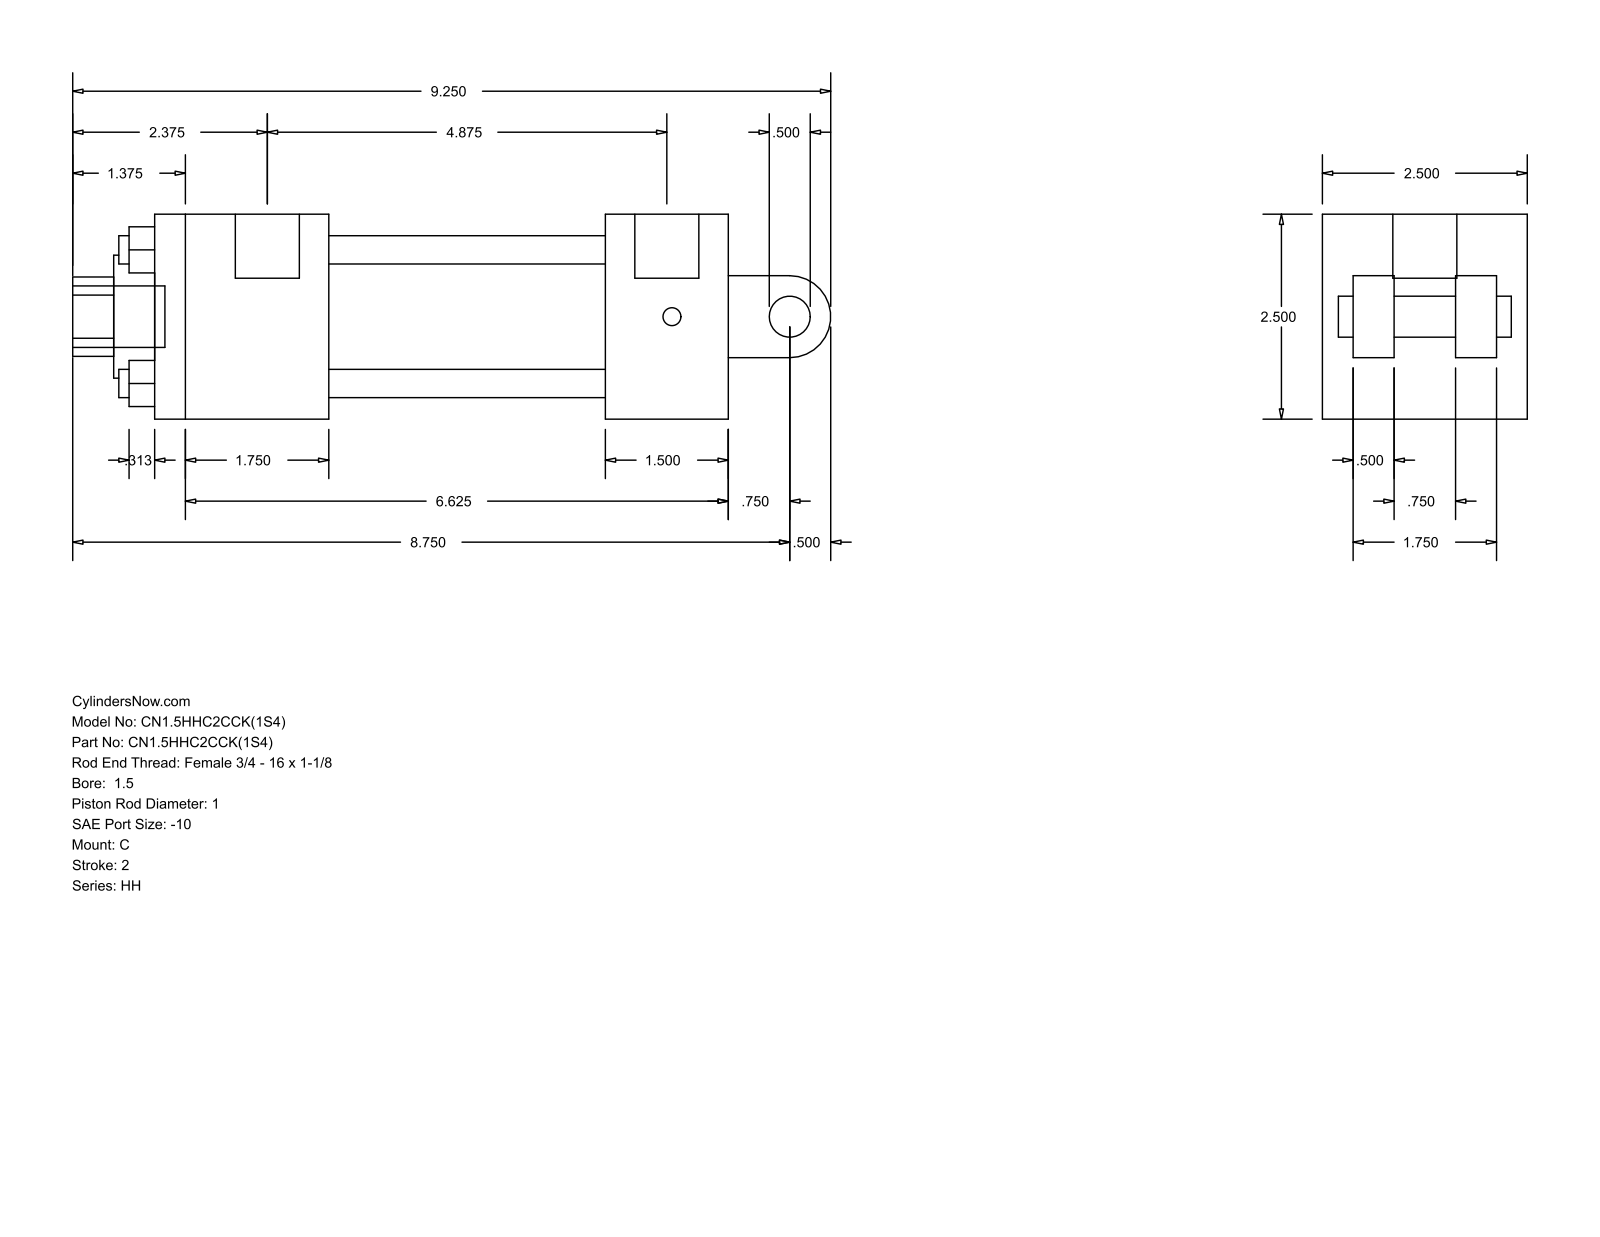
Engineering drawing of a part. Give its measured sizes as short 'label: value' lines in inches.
name: HH_C__0150_1
written by: GSSL Pune (CONFIG_CONTROL_DESIGN)
unit: in
bodies: 0 solids, 99 faces (70 planar, 29 cylindrical, 0 other)
size: 9.25 × 2.5 × 2.5
holes: 4× ⌀0.345, 2× ⌀0.219, 1× ⌀0.781, 1× ⌀1, 1× ⌀1.5, 1× ⌀1.75
bosses: 2× ⌀0.219, 1× ⌀0.781, 1× ⌀0.75, 1× ⌀0.5
rounds: 1× R0.484, 1× R0.5
face distances: 2.5, 2.125, 3.375, 4.875, 1.5, 5.5, 7, 0.5, 0.875, 1.625
hole spacings: 1.152, 1.63, 2.305, 0.063
